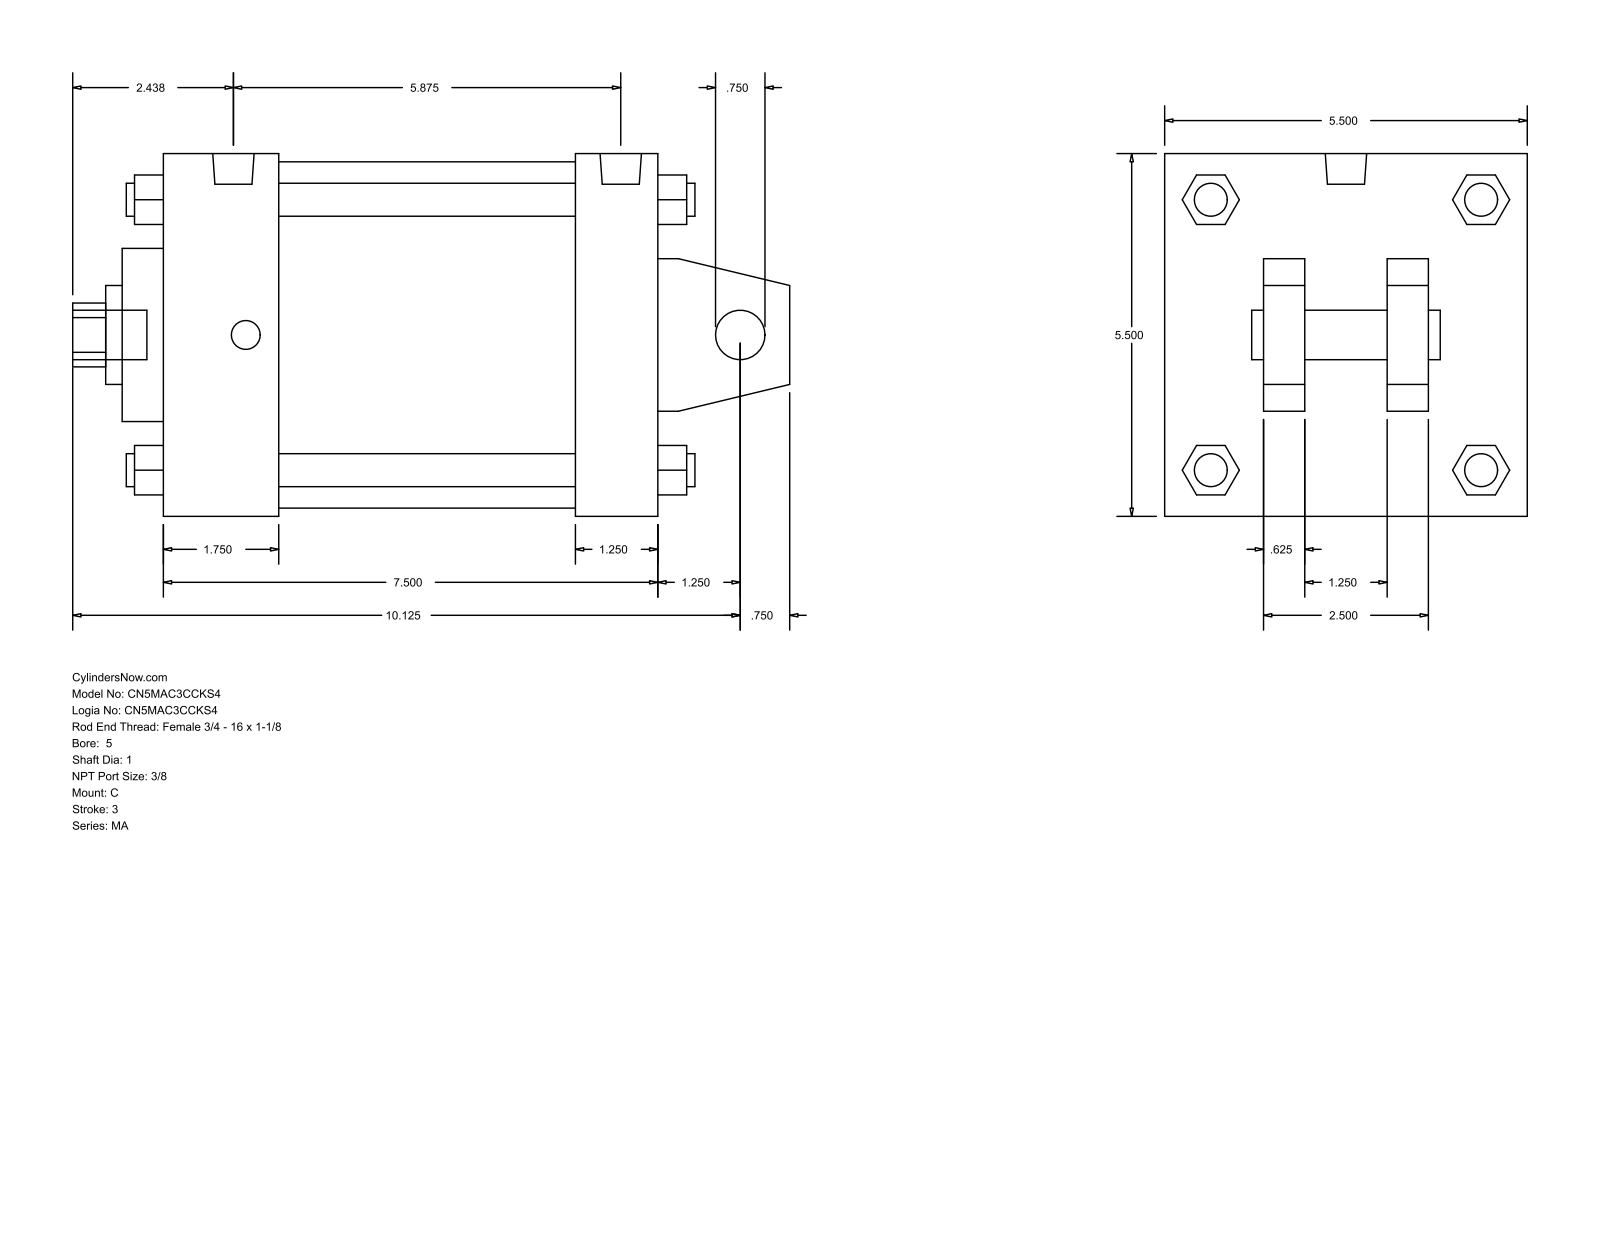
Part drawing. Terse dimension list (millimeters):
name: MA_C__0500_1
written by: GSSL Pune (CONFIG_CONTROL_DESIGN)
unit: mm
bodies: 0 solids, 141 faces (109 planar, 32 cylindrical, 0 other)
size: 276.23 × 139.7 × 139.7
holes: 1× ⌀19.05, 1× ⌀25.4, 1× ⌀38.1, 1× ⌀66.67, 1× ⌀133.35
bosses: 4× ⌀12.7, 4× ⌀11.11, 2× ⌀15.93, 1× ⌀19.05
rounds: 1× R12.29
face distances: 139.7, 190.51, 15.87, 158.76, 31.75, 44.46, 114.3, 146.05, 38.1, 101.6
